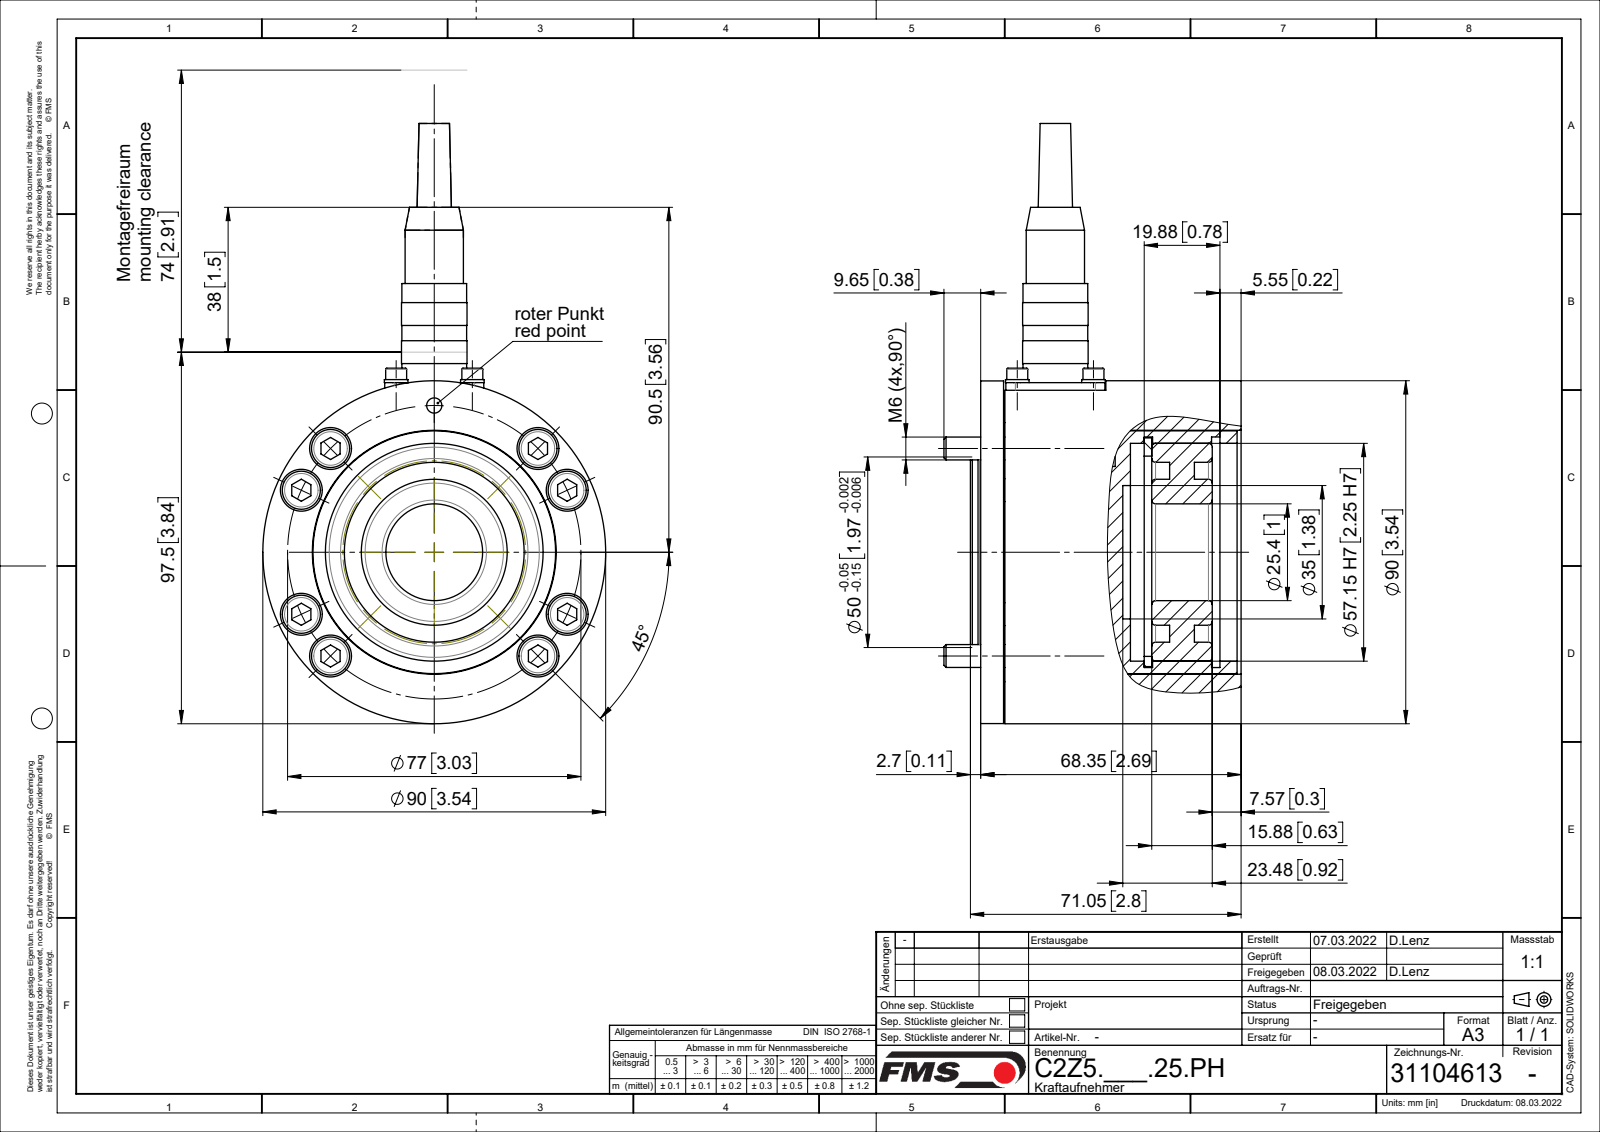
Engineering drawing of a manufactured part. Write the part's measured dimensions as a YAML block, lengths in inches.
part_name: "Kabeldose_M14x1_Mini_5pol; PKL_NLJ1_vereinfacht_01; Flanschstecker_M14x1_Mini_5pol; Zyl-Schr DIN912_M3x6 (+8 more)"
step_written_by: "SolidWorks 2018 (CONFIG_CONTROL_DESIGN)"
units: inches
bodies: {solids: 23, faces: 578, planar: 206, cylindrical: 258, other: 114}
overall_size: [6.201, 3.543, 3.071]
volume: 18.61
surface_area: 187.6
round_holes:
  - {diameter: 0.256, count: 8}
  - {diameter: 0.433, count: 8}
  - {diameter: 0.098, count: 6}
  - {diameter: 0.122, count: 4}
  - {diameter: 0.126, count: 4}
  - {diameter: 0.197, count: 4}
  - {diameter: 0.276, count: 4}
  - {diameter: 0.157, count: 2}
  - {diameter: 0.402, count: 1}
  - {diameter: 0.472, count: 1}
  - {diameter: 0.591, count: 1}
  - {diameter: 0.709, count: 1}
round_bosses_or_shafts:
  - {diameter: 0.394, count: 8}
  - {diameter: 0.236, count: 8}
  - {diameter: 0.059, count: 5}
  - {diameter: 0.244, count: 4}
  - {diameter: 0.217, count: 4}
  - {diameter: 0.118, count: 4}
  - {diameter: 3.543, count: 1}
  - {diameter: 3.539, count: 1}
partial_cylinders:
  - {radius: 0.004, count: 4}
  - {radius: 0.098, count: 4}
  - {radius: 0.164, count: 2}
  - {radius: 0.197, count: 2}
  - {radius: 0.913, count: 1}
  - {radius: 1.035, count: 1}
face_to_face_distances: [0.236, 0.13, 0.106, 1.301, 1.26, 0.079, 1.496, 1.181, 1.154, 1.39]
hole_center_spacings: [0.787, 1.516, 0.526, 0.557, 1.515, 1.739, 2.143, 2.483]
